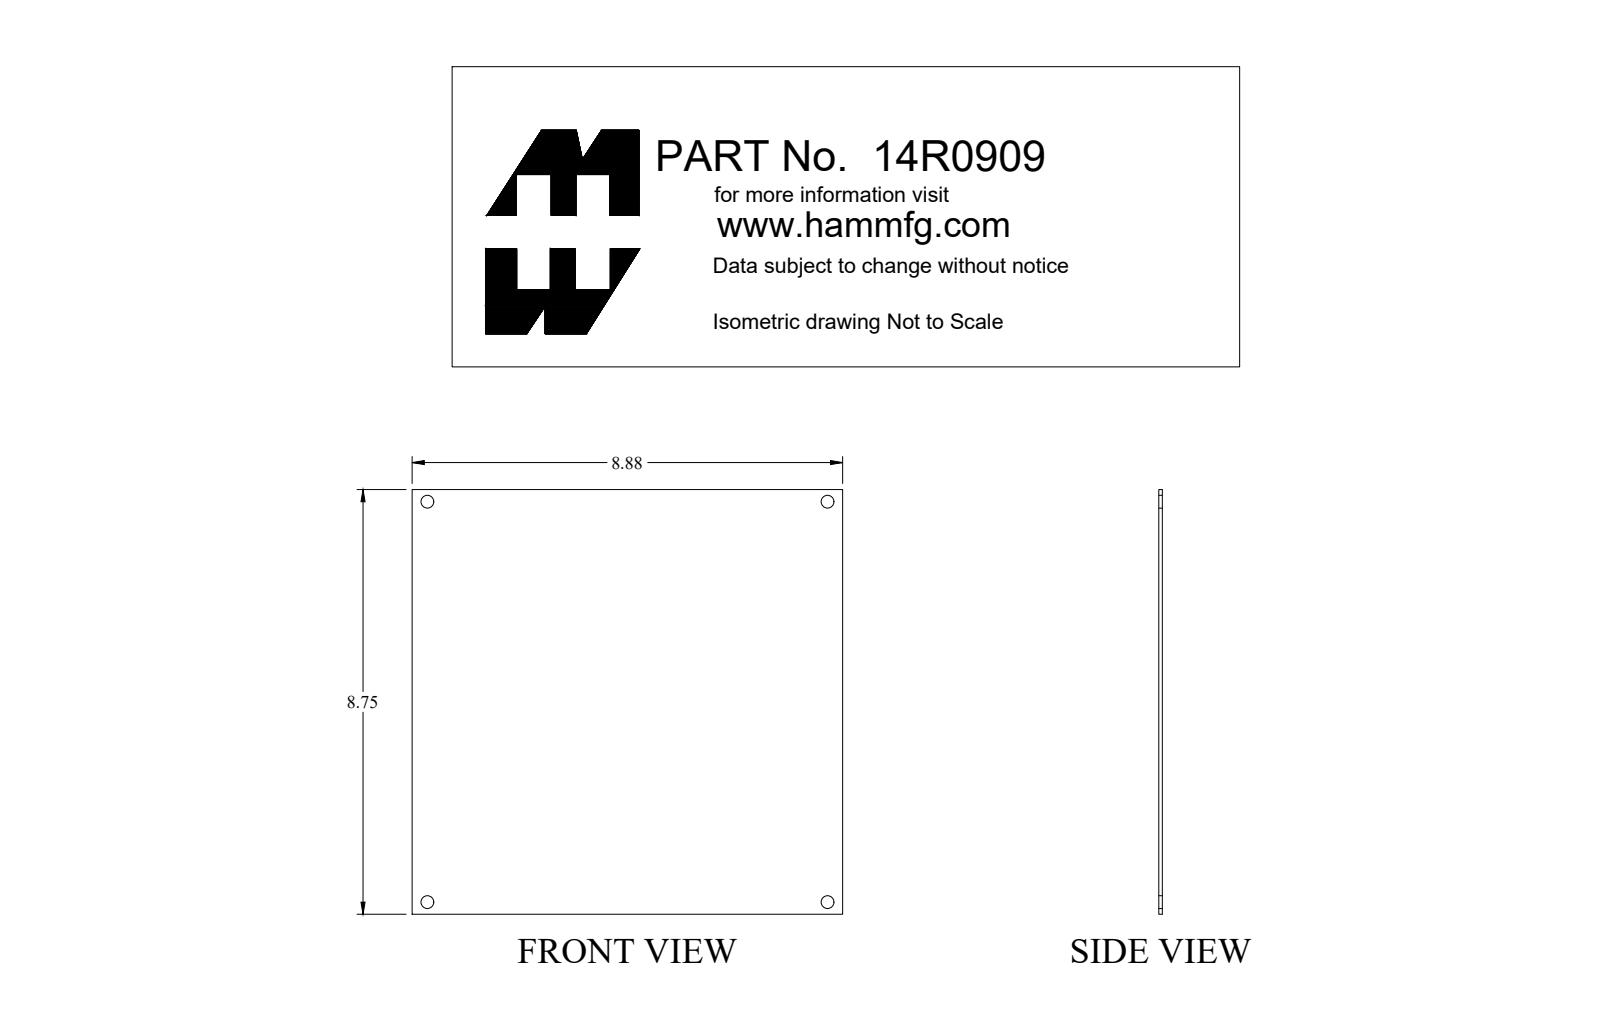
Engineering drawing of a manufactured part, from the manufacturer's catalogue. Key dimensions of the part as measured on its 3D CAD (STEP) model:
Part name (STEP PRODUCT): 14R0909
STEP written by: SolidWorks 2018 (AUTOMOTIVE_DESIGN)
Units: inches
Bodies: 1 solid, 10 faces (6 planar, 4 cylindrical, 0 other)
Overall size (bounding box): 8.875 × 8.75 × 0.072
Volume: 5.575 in³ · Surface area: 157.6 in²
Round holes (diameter × count): ⌀0.265 ×4
Main face-to-face distances: 0.072, 8.75, 8.875
Hole centre spacings: 8.25, 11.667
